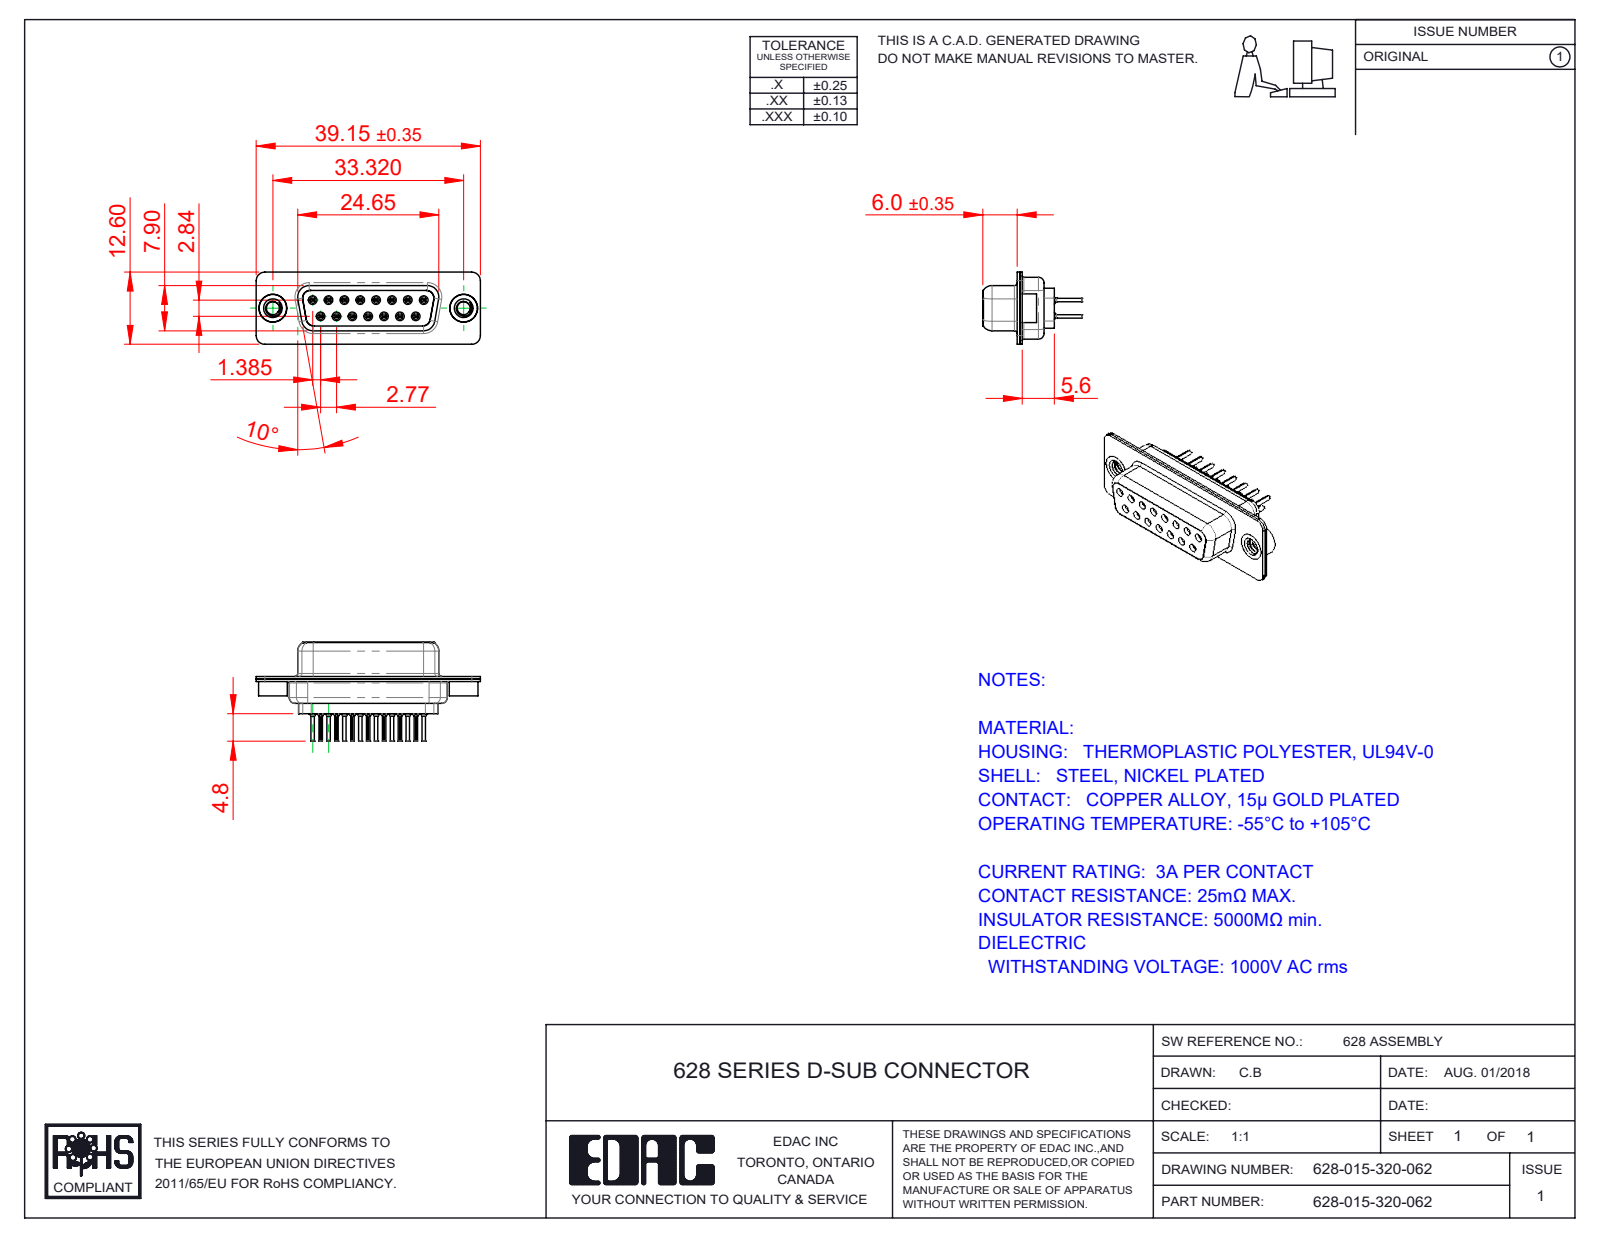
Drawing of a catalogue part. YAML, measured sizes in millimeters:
part_name: "628 Shell Rear_15 Contacts; 628 4-40 Threaded Rivet; 628 Shell Front_15 Contacts; 628-015-320-062 (+3 more)"
step_written_by: "SolidWorks 2020 (CONFIG_CONTROL_DESIGN)"
units: millimeters
bodies: {solids: 20, faces: 2180, planar: 532, cylindrical: 630, other: 1018}
overall_size: [39.15, 17.3, 12.6]
volume: 2538
surface_area: 6315
round_holes:
  - {diameter: 0.2, count: 15}
  - {diameter: 0.8, count: 15}
  - {diameter: 0.9, count: 15}
  - {diameter: 1.1, count: 15}
  - {diameter: 1.6, count: 15}
  - {diameter: 1.7, count: 8}
  - {diameter: 2.26, count: 2}
  - {diameter: 4, count: 2}
  - {diameter: 4.05, count: 2}
  - {diameter: 4.85, count: 2}
round_bosses_or_shafts:
  - {diameter: 2, count: 15}
  - {diameter: 1.5, count: 15}
  - {diameter: 1.2, count: 15}
  - {diameter: 0.6, count: 15}
  - {diameter: 5, count: 2}
  - {diameter: 4.95, count: 2}
  - {diameter: 4.8, count: 2}
partial_cylinders:
  - {radius: 0.1, count: 30}
  - {radius: 1.5, count: 18}
  - {radius: 0.28, count: 15}
  - {radius: 2, count: 12}
  - {radius: 1.35, count: 8}
  - {radius: 0.25, count: 4}
  - {radius: 0.5, count: 4}
  - {radius: 0.6, count: 4}
face_to_face_distances: [0.45, 0.4, 0.9, 6.6, 1.9, 8.5, 1.4, 0.85, 7.05, 7.45]
hole_center_spacings: [3.16, 2.77, 5.54, 8.31, 11.08, 5.03, 5.04, 7.48]
